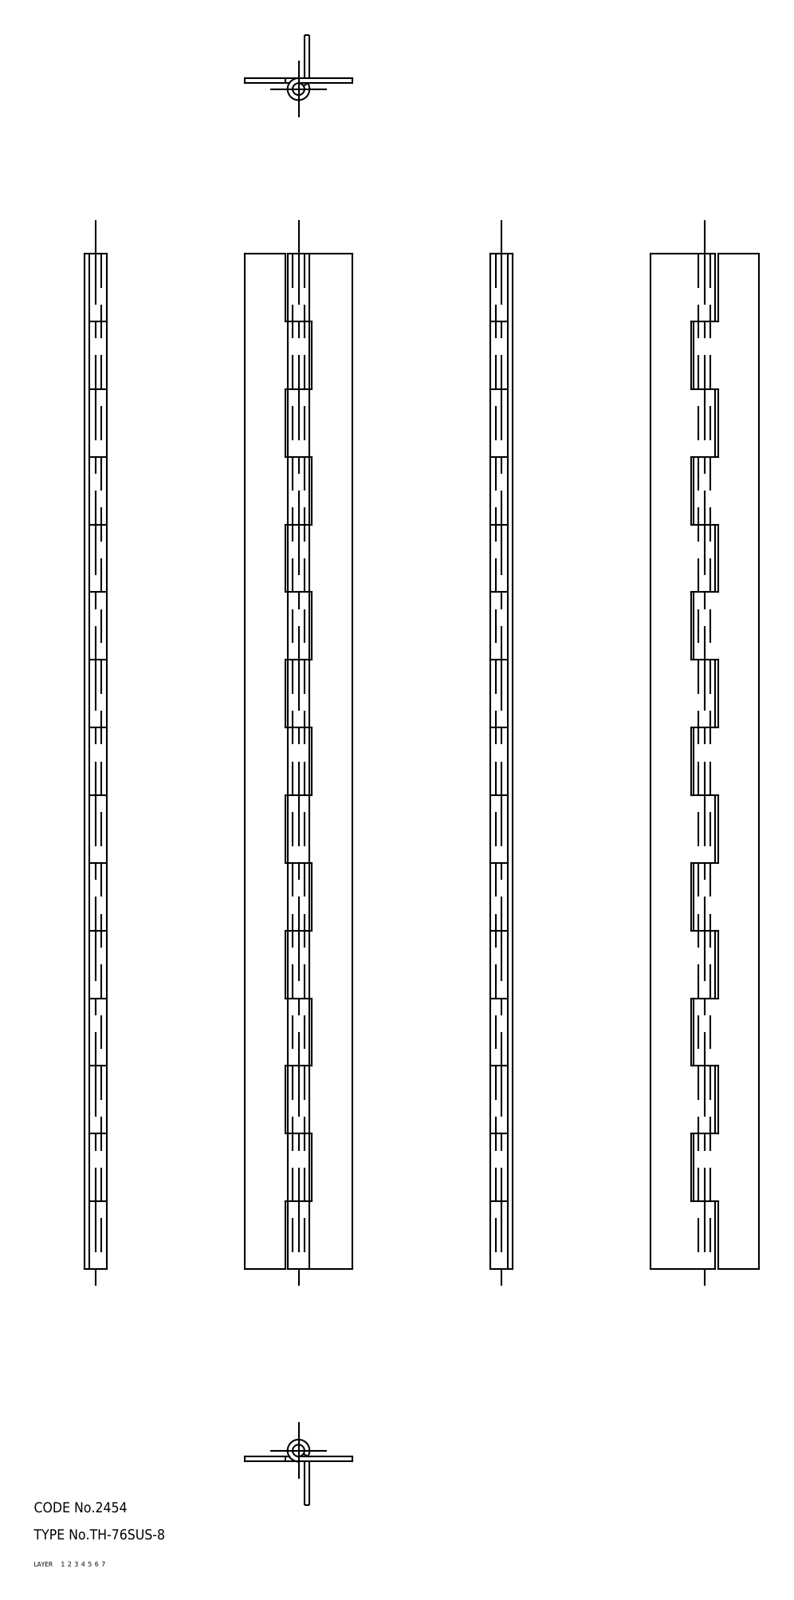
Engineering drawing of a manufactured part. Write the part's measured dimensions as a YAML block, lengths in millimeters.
part_name: "shaft; hinge piece_B; hinge piece_A; TH_76SUS_8_15841_36"
step_written_by: "CADfix (AUTOMOTIVE_DESIGN)"
units: millimeters
bodies: {solids: 3, faces: 102, planar: 0, cylindrical: 0, other: 102}
overall_size: [300, 32, 6.5]
volume: 21413
surface_area: 30660
